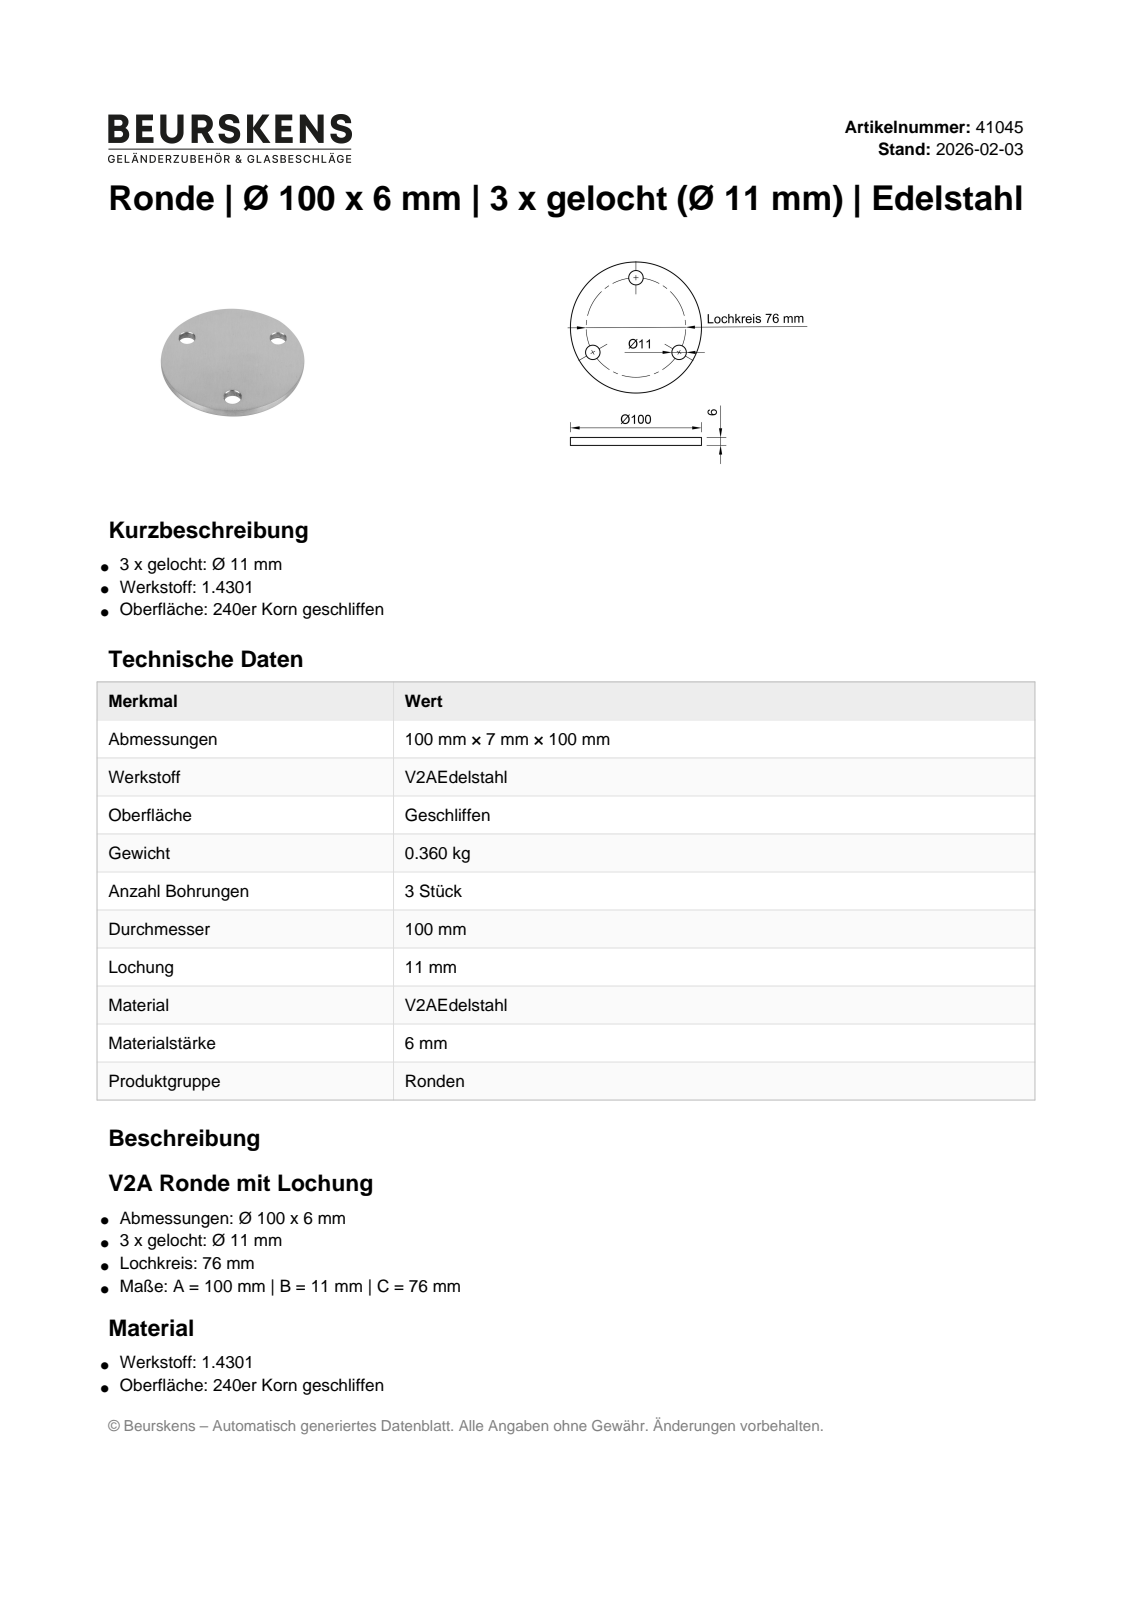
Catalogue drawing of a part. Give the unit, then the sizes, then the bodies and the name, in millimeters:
Units: millimetres
Overall size (bounding box): 100 × 100 × 6
Round holes (diameter × count): ⌀11 ×3
Round bosses / shafts (diameter × count): ⌀100 ×1
Main face-to-face distances: 6
Hole centre spacings: 65.82
Volume: 45 413 mm³ · Surface area: 17 645 mm²
Bodies: 1 solid, 6 faces (2 planar, 4 cylindrical, 0 other)
Part name (STEP PRODUCT): 41045
STEP written by: Autodesk Inventor 2022 (AUTOMOTIVE_DESIGN)
